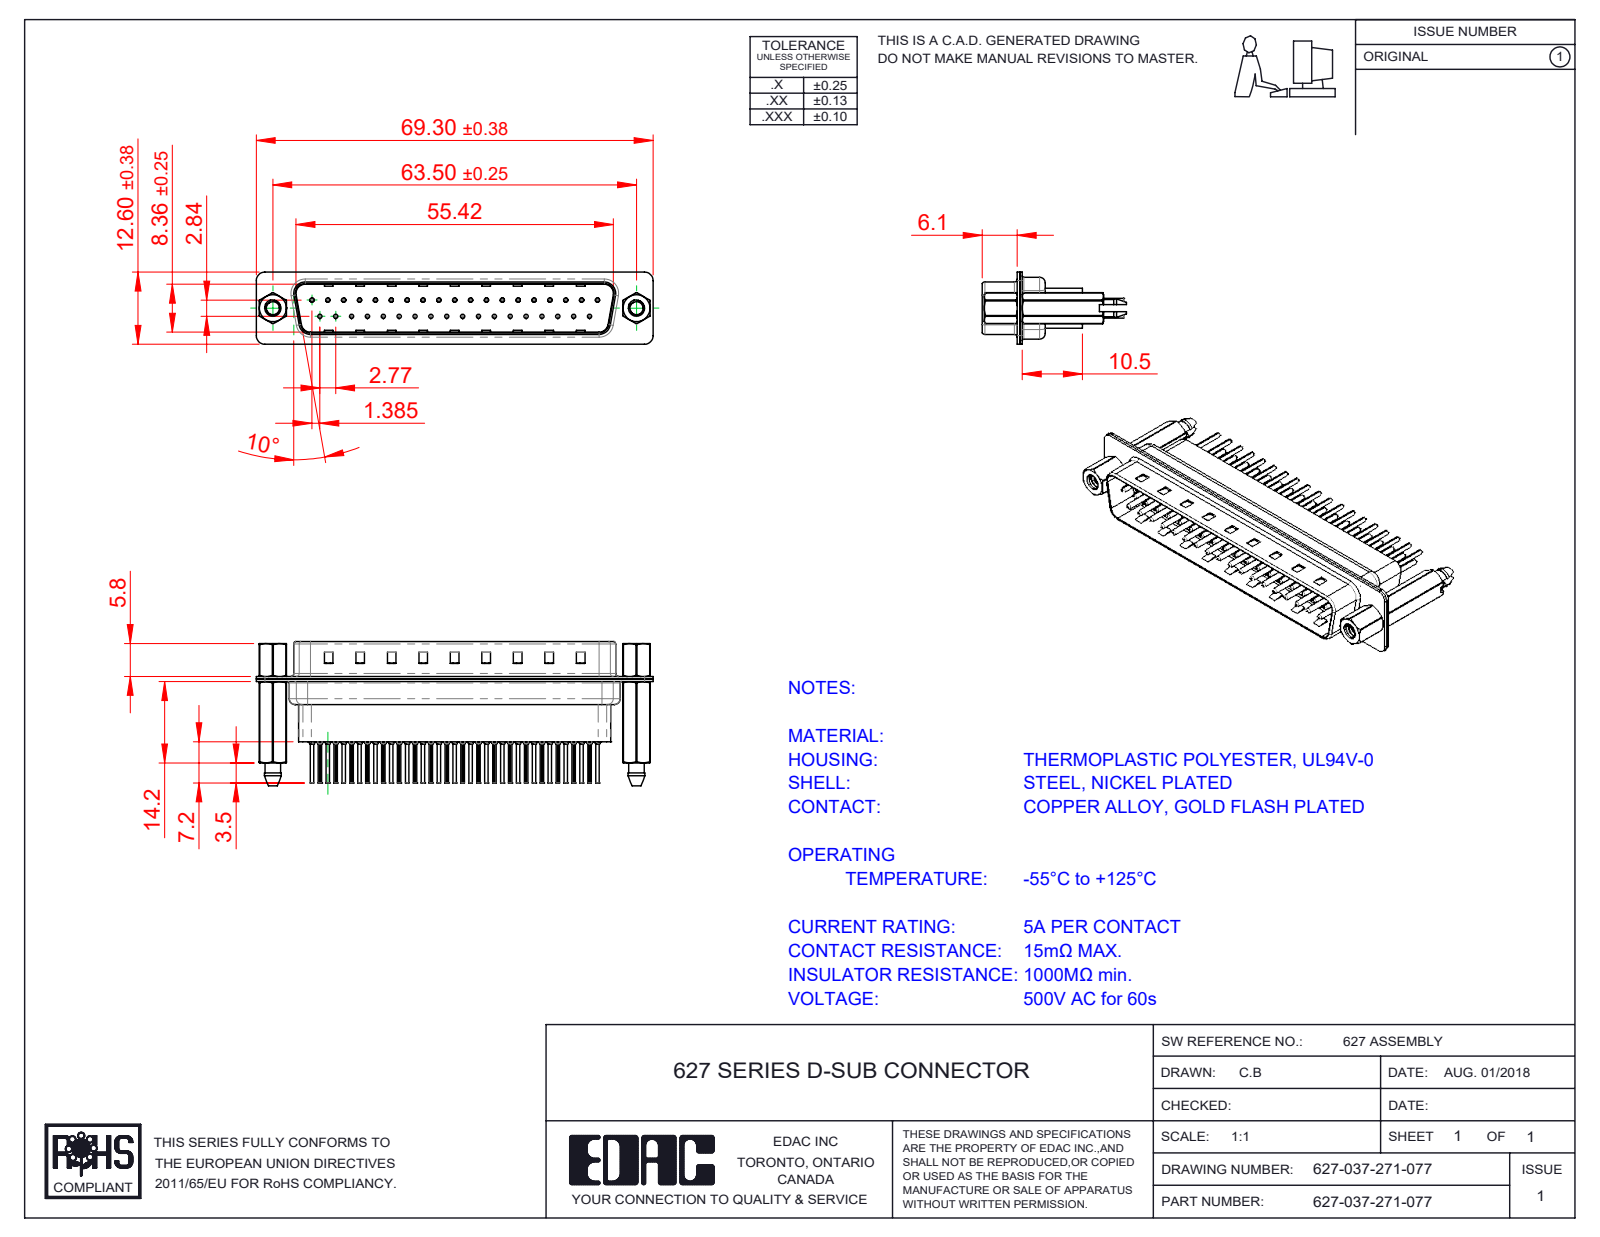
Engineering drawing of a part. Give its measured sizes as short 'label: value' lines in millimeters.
name: 627 4-40 Hex Standoff; 627 Housing_37 HP; 627 Shell Front_37 Contacts; 627 Shell Rear_37 Contacts (+4 more)
written by: SolidWorks 2020 (CONFIG_CONTROL_DESIGN)
unit: mm
bodies: 44 solids, 4272 faces (1145 planar, 1648 cylindrical, 1479 other)
size: 69.3 × 25.1 × 12.6
volume: 5 911 mm³; area: 15 189 mm²
holes: 37× ⌀0.2, 37× ⌀0.35, 37× ⌀1.1, 37× ⌀1.6, 2× ⌀2.26, 2× ⌀2.29, 2× ⌀4, 2× ⌀4.8
bosses: 37× ⌀2, 37× ⌀1.5, 37× ⌀0.75, 37× ⌀0.6, 2× ⌀4.9, 2× ⌀2.79
rounds: 74× R0.1, 18× R1.5, 12× R2, 10× R1.6, 8× R0.5, 4× R0.25, 4× R0.6, 4× R0.65
face distances: 0.4, 0.82, 9.58, 0.45, 0.68, 7.68, 1.5, 1.08, 8.08, 8.76
hole spacings: 3.16, 2.77, 5.54, 8.31, 5.04, 10.1, 11.08, 12.78
